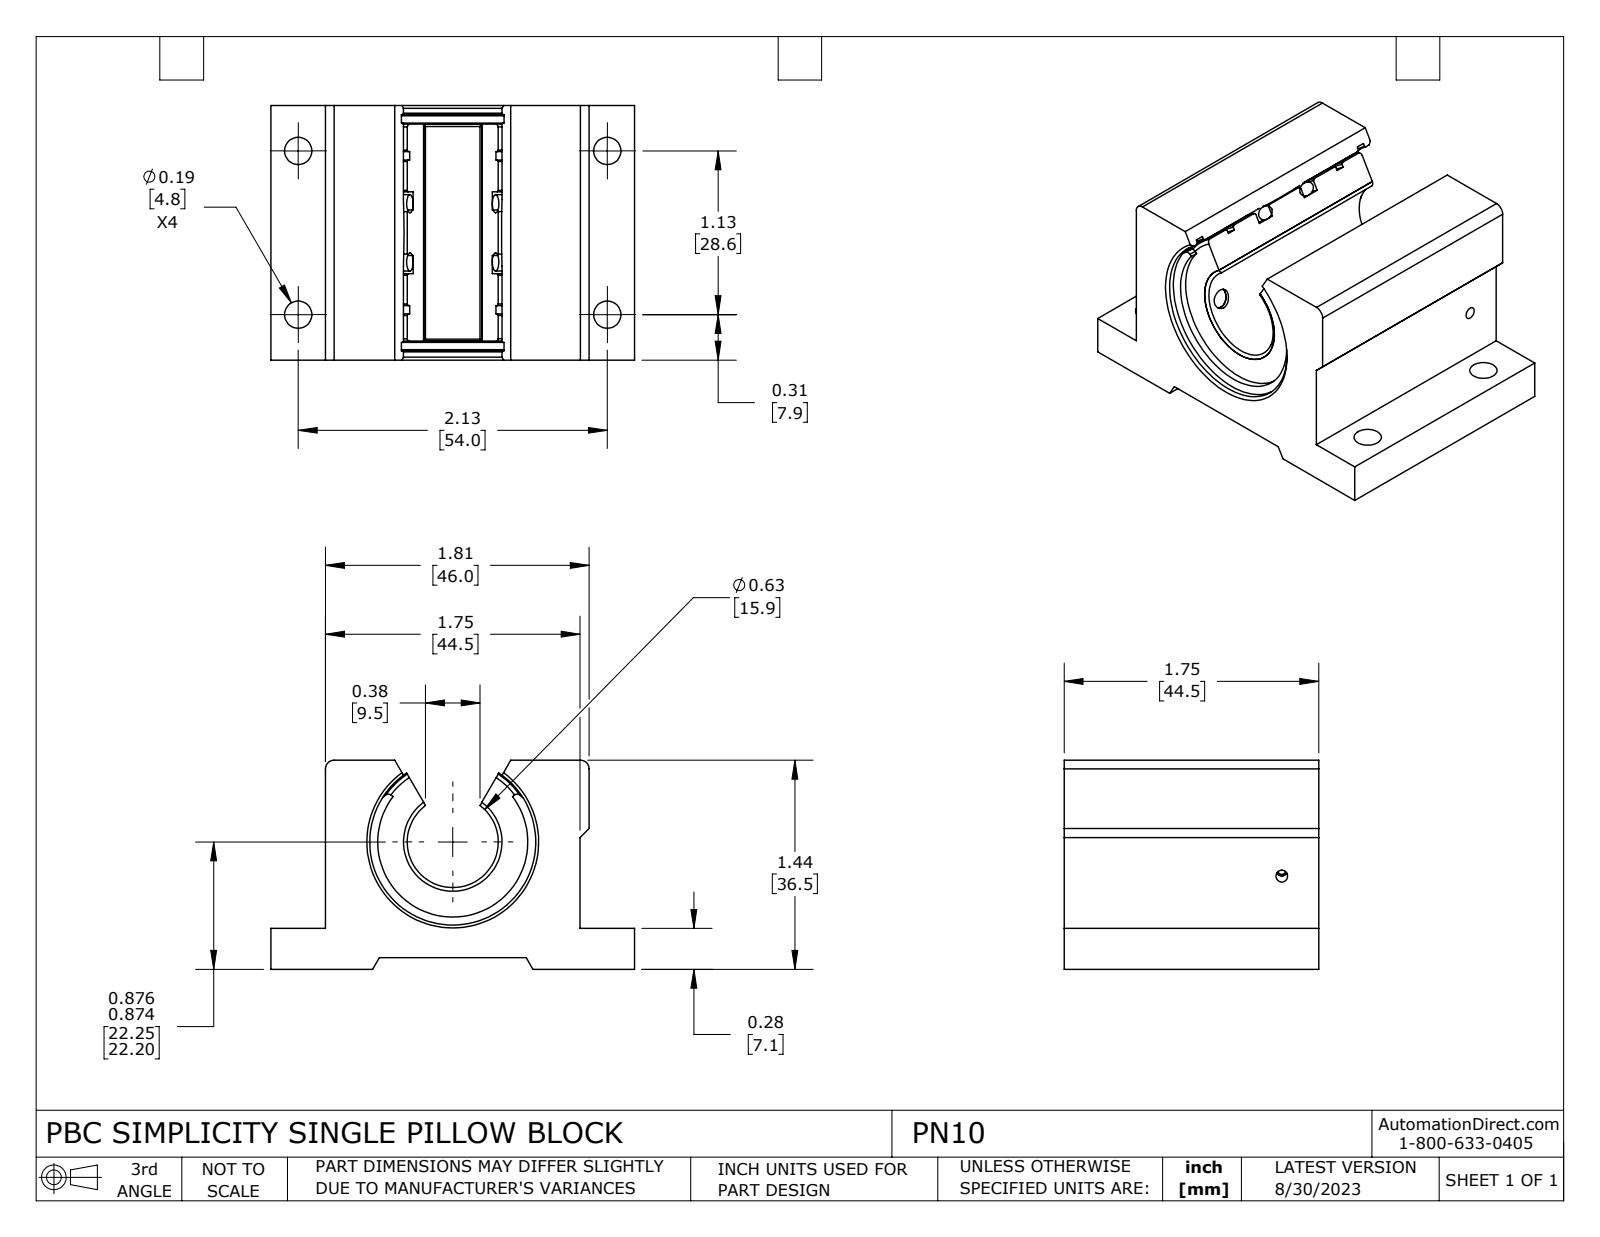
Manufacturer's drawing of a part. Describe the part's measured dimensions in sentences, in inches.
The part is named "PN10". Its 3-D file was written by "SolidWorks 2021 (CONFIG_CONTROL_DESIGN)". It is 8 solids with 207 faces: 54 planar, 94 cylindrical and 59 other. Overall it measures 2.5 by 1.75 by 1.437 inches. Its volume is 3.629 cubic inches and its surface area 39.82 square inches. Round holes: 4 of diameter 0.187, 1 of diameter 0.054, 1 of diameter 0.079, 1 of diameter 0.136, 1 of diameter 0.626, 1 of diameter 0.677, 1 of diameter 1.141, 1 of diameter 1.197. Round bosses or shafts: 1 of diameter 1.124, 1 of diameter 1.06, 1 of diameter 0.962, 1 of diameter 0.078. Partial cylindrical surfaces (rounded edges, fillets, slot ends): 2 of radius 0.03, 2 of radius 0.06, 2 of radius 0.18, 1 of radius 0.516, 1 of radius 0.609. The main face-to-face distances are 1.75, 0.08, 1.437, 1.357, 0.281, 0.201, 1.156, 0.375, 2.125, 0.129. The hole center spacings are 1.125, 2.125, 2.405.
